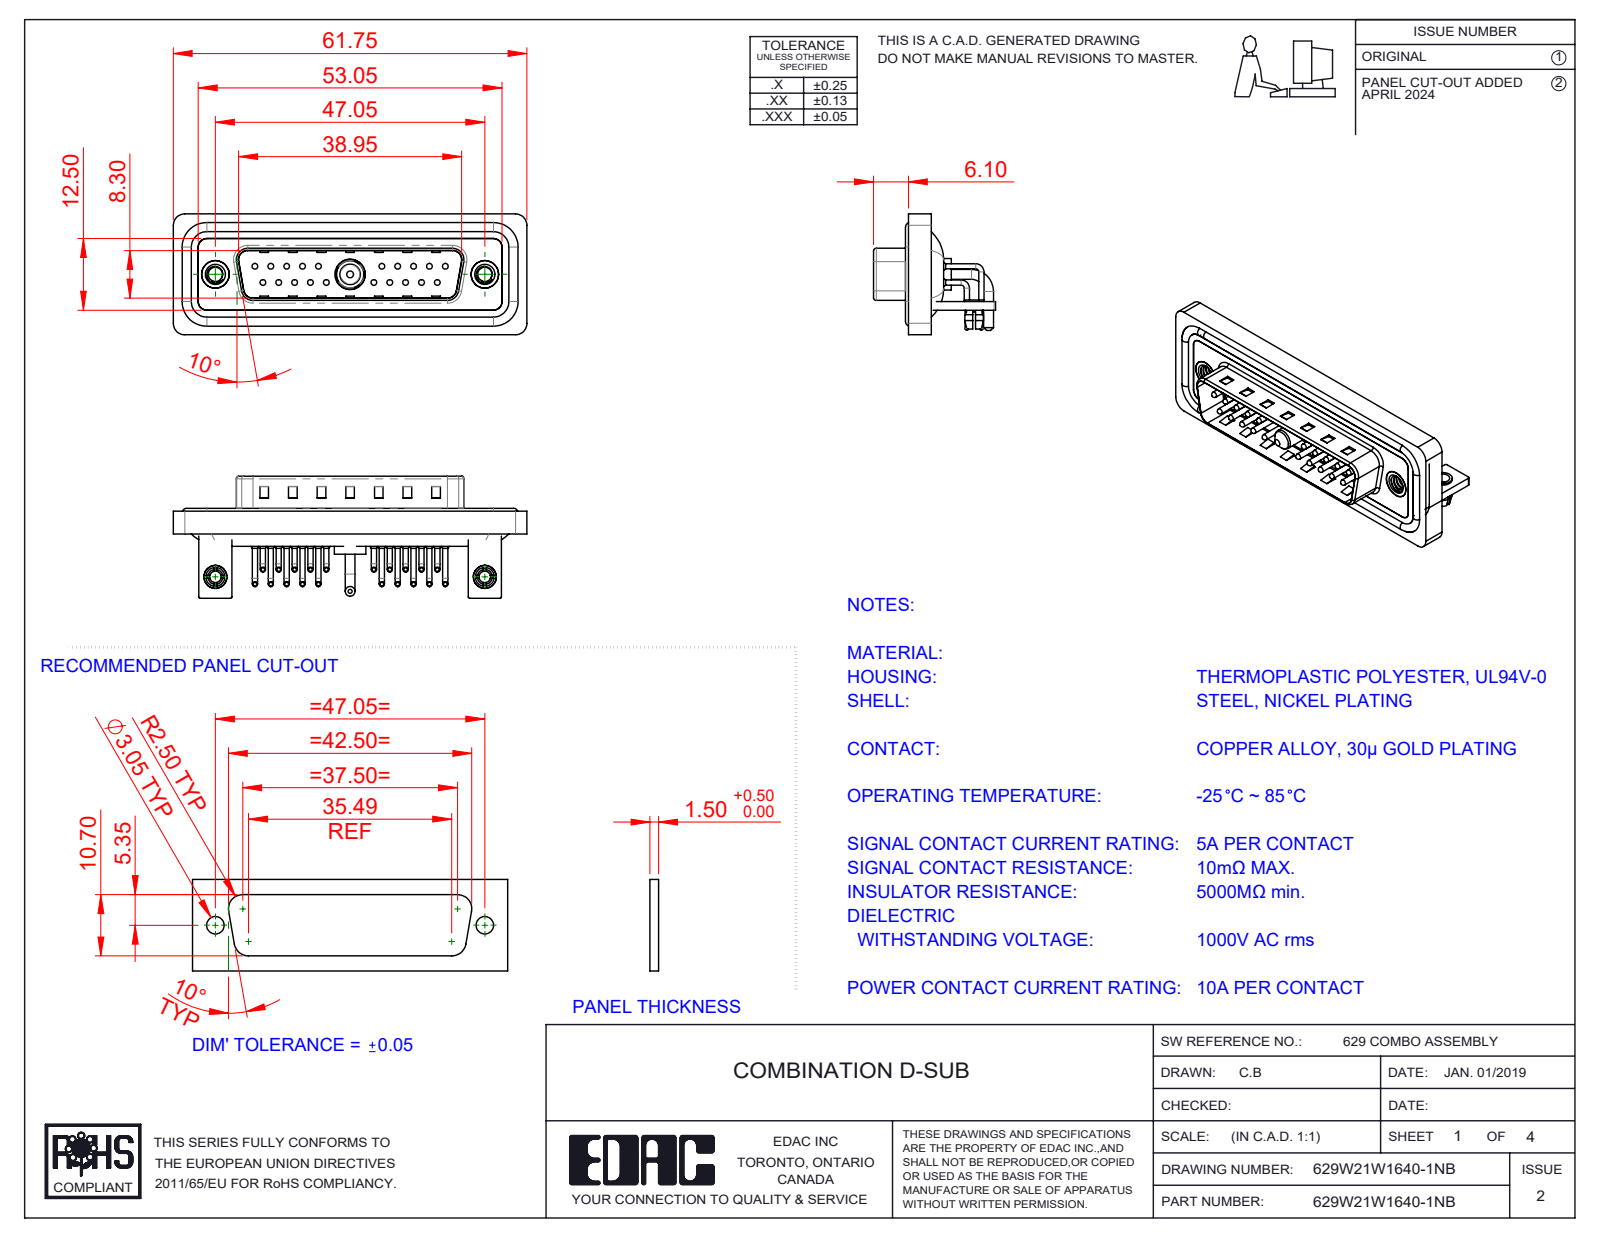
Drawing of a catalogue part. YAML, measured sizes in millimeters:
part_name: "629W21W1640-1NB; 629Combo Housing_21W1; 629Combo Contact Row 1; 629Combo Stabilizer Bracket (+7 more)"
step_written_by: "SolidWorks 2023 (CONFIG_CONTROL_DESIGN)"
units: millimeters
bodies: {solids: 33, faces: 2856, planar: 1567, cylindrical: 979, other: 310}
overall_size: [61.75, 21.3, 21.1]
volume: 7668
surface_area: 13468
round_holes:
  - {diameter: 2, count: 22}
  - {diameter: 0.75, count: 20}
  - {diameter: 1.6, count: 20}
  - {diameter: 2.5, count: 4}
  - {diameter: 3.2, count: 2}
  - {diameter: 4, count: 2}
  - {diameter: 4.8, count: 2}
  - {diameter: 5, count: 2}
  - {diameter: 4.85, count: 1}
  - {diameter: 5.3, count: 1}
round_bosses_or_shafts:
  - {diameter: 0.9, count: 40}
  - {diameter: 1.5, count: 20}
  - {diameter: 1, count: 20}
  - {diameter: 0.65, count: 20}
  - {diameter: 1.6, count: 4}
  - {diameter: 4.9, count: 2}
  - {diameter: 4, count: 2}
  - {diameter: 3.4, count: 2}
partial_cylinders:
  - {radius: 1.01, count: 20}
  - {radius: 2, count: 19}
  - {radius: 1.5, count: 18}
  - {radius: 0.25, count: 16}
  - {radius: 0.5, count: 9}
  - {radius: 1.6, count: 8}
  - {radius: 0.6, count: 4}
  - {radius: 0.65, count: 4}
face_to_face_distances: [0.4, 0.8, 2.1, 2.9, 1.5, 1.1, 4.1, 1.6, 4.5, 3.7]
hole_center_spacings: [3.16, 2.77, 5.54, 8.31, 5.04, 19.39, 20.97, 22.16]
